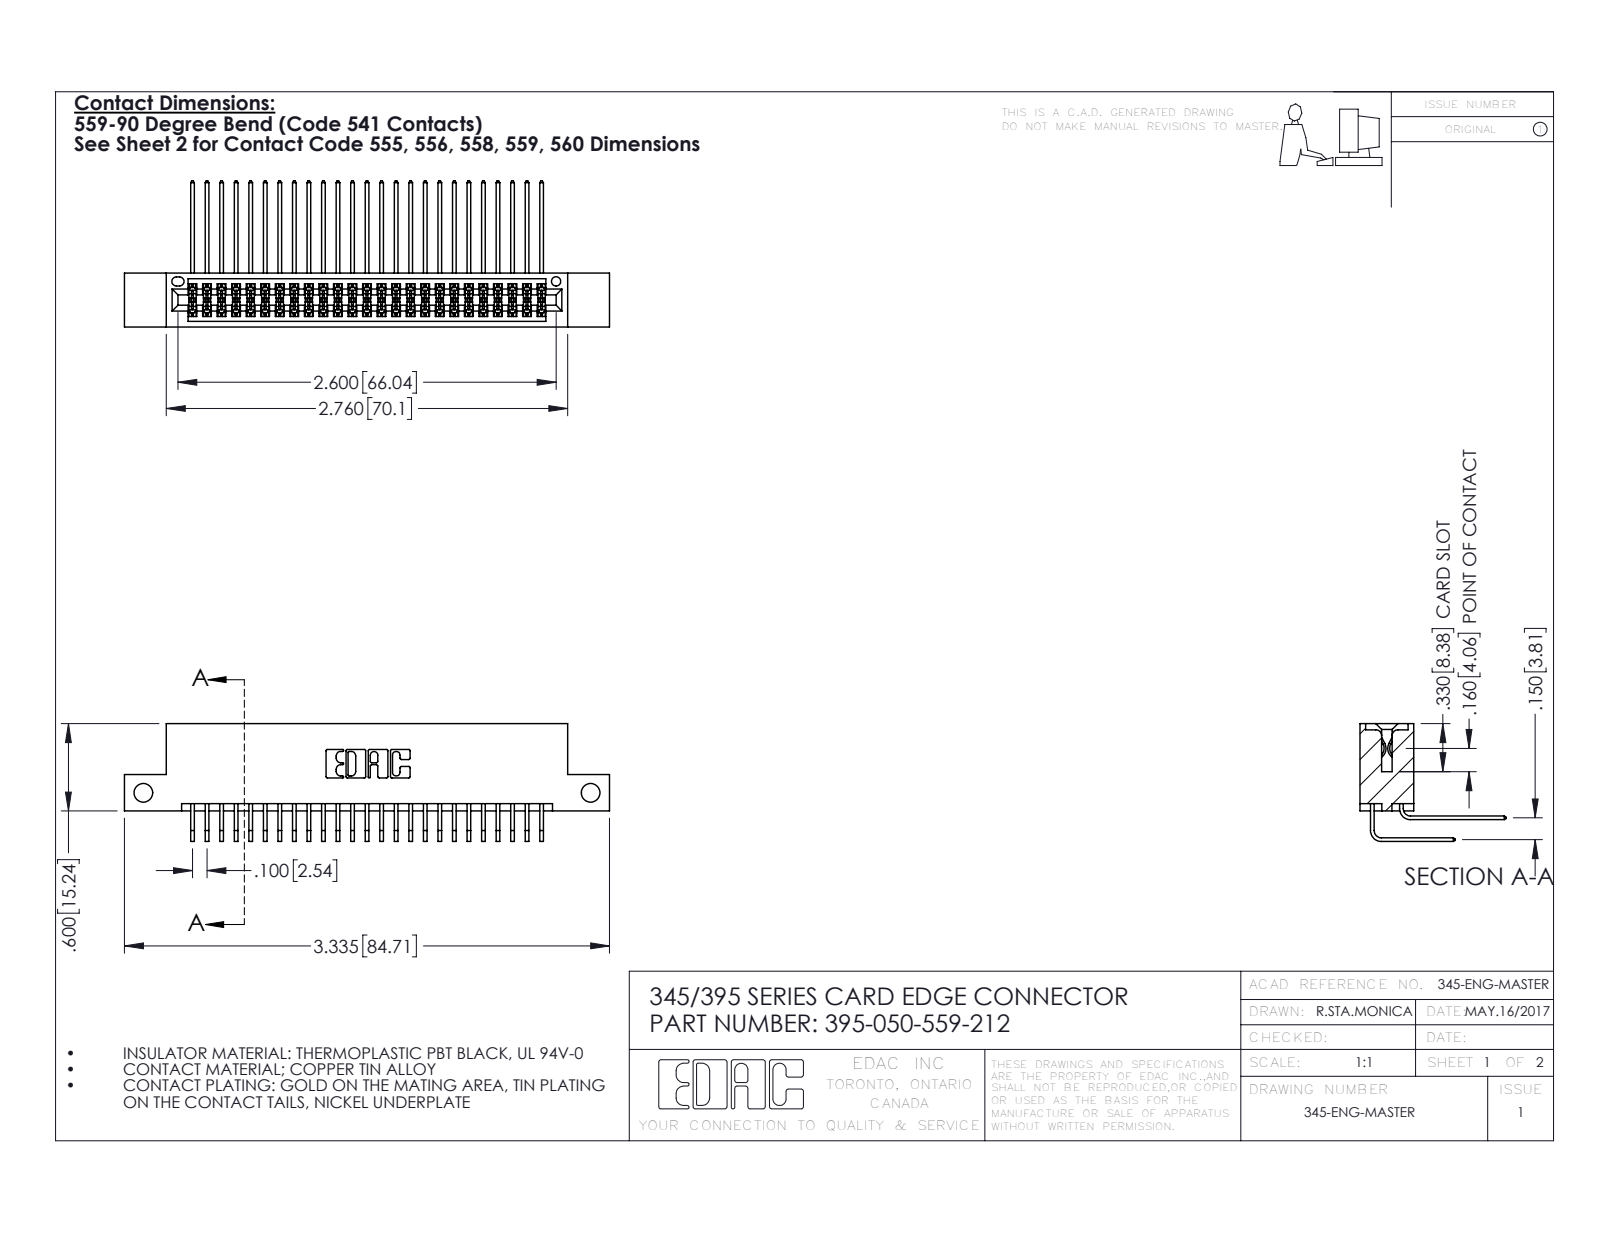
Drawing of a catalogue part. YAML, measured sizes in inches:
part_name: "345 Part_Flush Mounting Lugs - Side Mount; 345-292-001_558 559 Tail - 1; 395-050-559-212; 345-292-001_559 Tail - 2"
step_written_by: "SolidWorks 2016 (CONFIG_CONTROL_DESIGN)"
units: inches
bodies: {solids: 51, faces: 2726, planar: 1830, cylindrical: 896, other: 0}
overall_size: [3.335, 1.005, 0.809]
volume: 0.505
surface_area: 20.33
round_holes:
  - {diameter: 0.128, count: 2}
  - {diameter: 0.064, count: 1}
partial_cylinders:
  - {radius: 0.006, count: 75}
  - {radius: 0.01, count: 22}
  - {radius: 0.007, count: 6}
  - {radius: 0.031, count: 6}
  - {radius: 0.026, count: 3}
  - {radius: 0.014, count: 2}
  - {radius: 0.019, count: 2}
  - {radius: 0.022, count: 2}
face_to_face_distances: [0.072, 0.298, 0.2, 0.37, 0.098, 0.272, 0.025, 0.225, 0.15, 0.175]
hole_center_spacings: [3.075]
